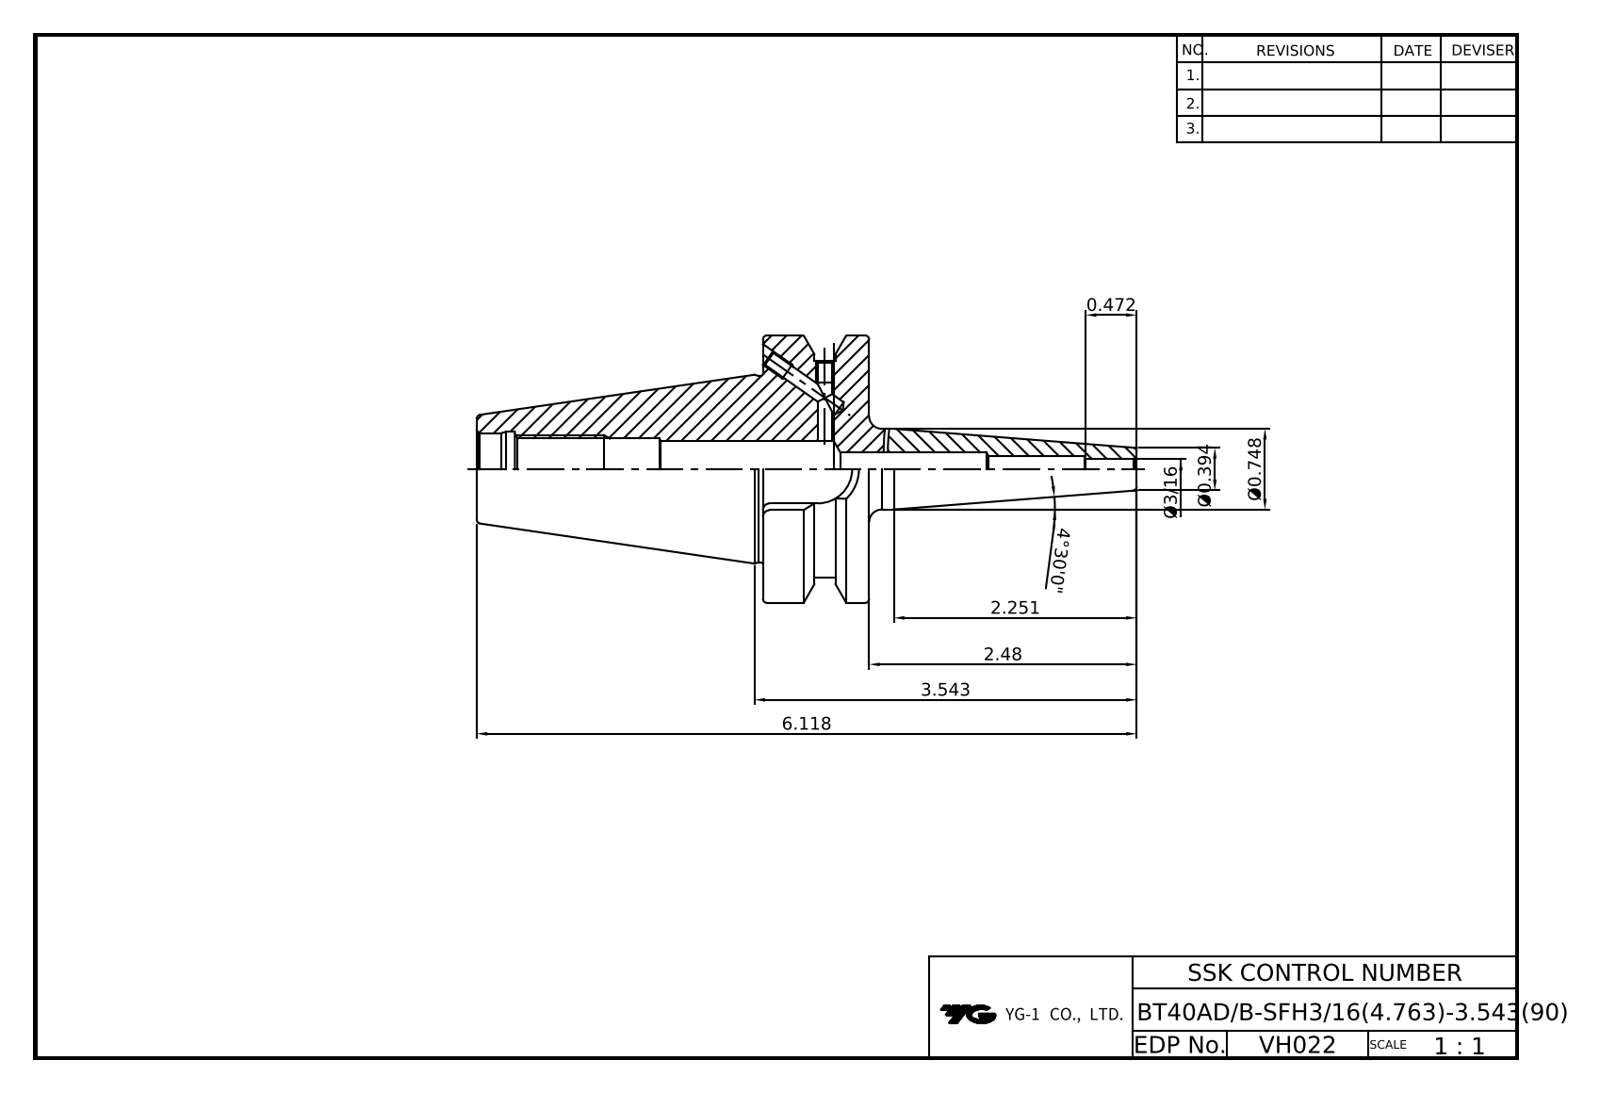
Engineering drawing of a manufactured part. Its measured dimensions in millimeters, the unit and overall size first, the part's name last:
Units: millimetres
Overall size (bounding box): 155.4 × 63 × 63
Round holes (diameter × count): ⌀4.76 ×1, ⌀6 ×1, ⌀8 ×1, ⌀13.5 ×1, ⌀14 ×1, ⌀16 ×1, ⌀17 ×1, ⌀17.6 ×1
Round bosses / shafts (diameter × count): ⌀63 ×1, ⌀51 ×1, ⌀44 ×1, ⌀19 ×1
Partial cylindrical surfaces — rounded edges, fillets, slot ends (radius × count): R8.05 ×1
Main face-to-face distances: 25, 45.2, 17.1, 7.9, 12.1, 5, 12.9, 16.1, 67.4, 79.5
Volume: 129 043 mm³ · Surface area: 27 760 mm²
Bodies: 1 solid, 92 faces (20 planar, 28 cylindrical, 44 other)
Part name (STEP PRODUCT): BT40ADB-SFH3_175-90
STEP written by: CREO PARAMETRIC BY PTC INC, 2018500 (CONFIG_CONTROL_DESIGN)
